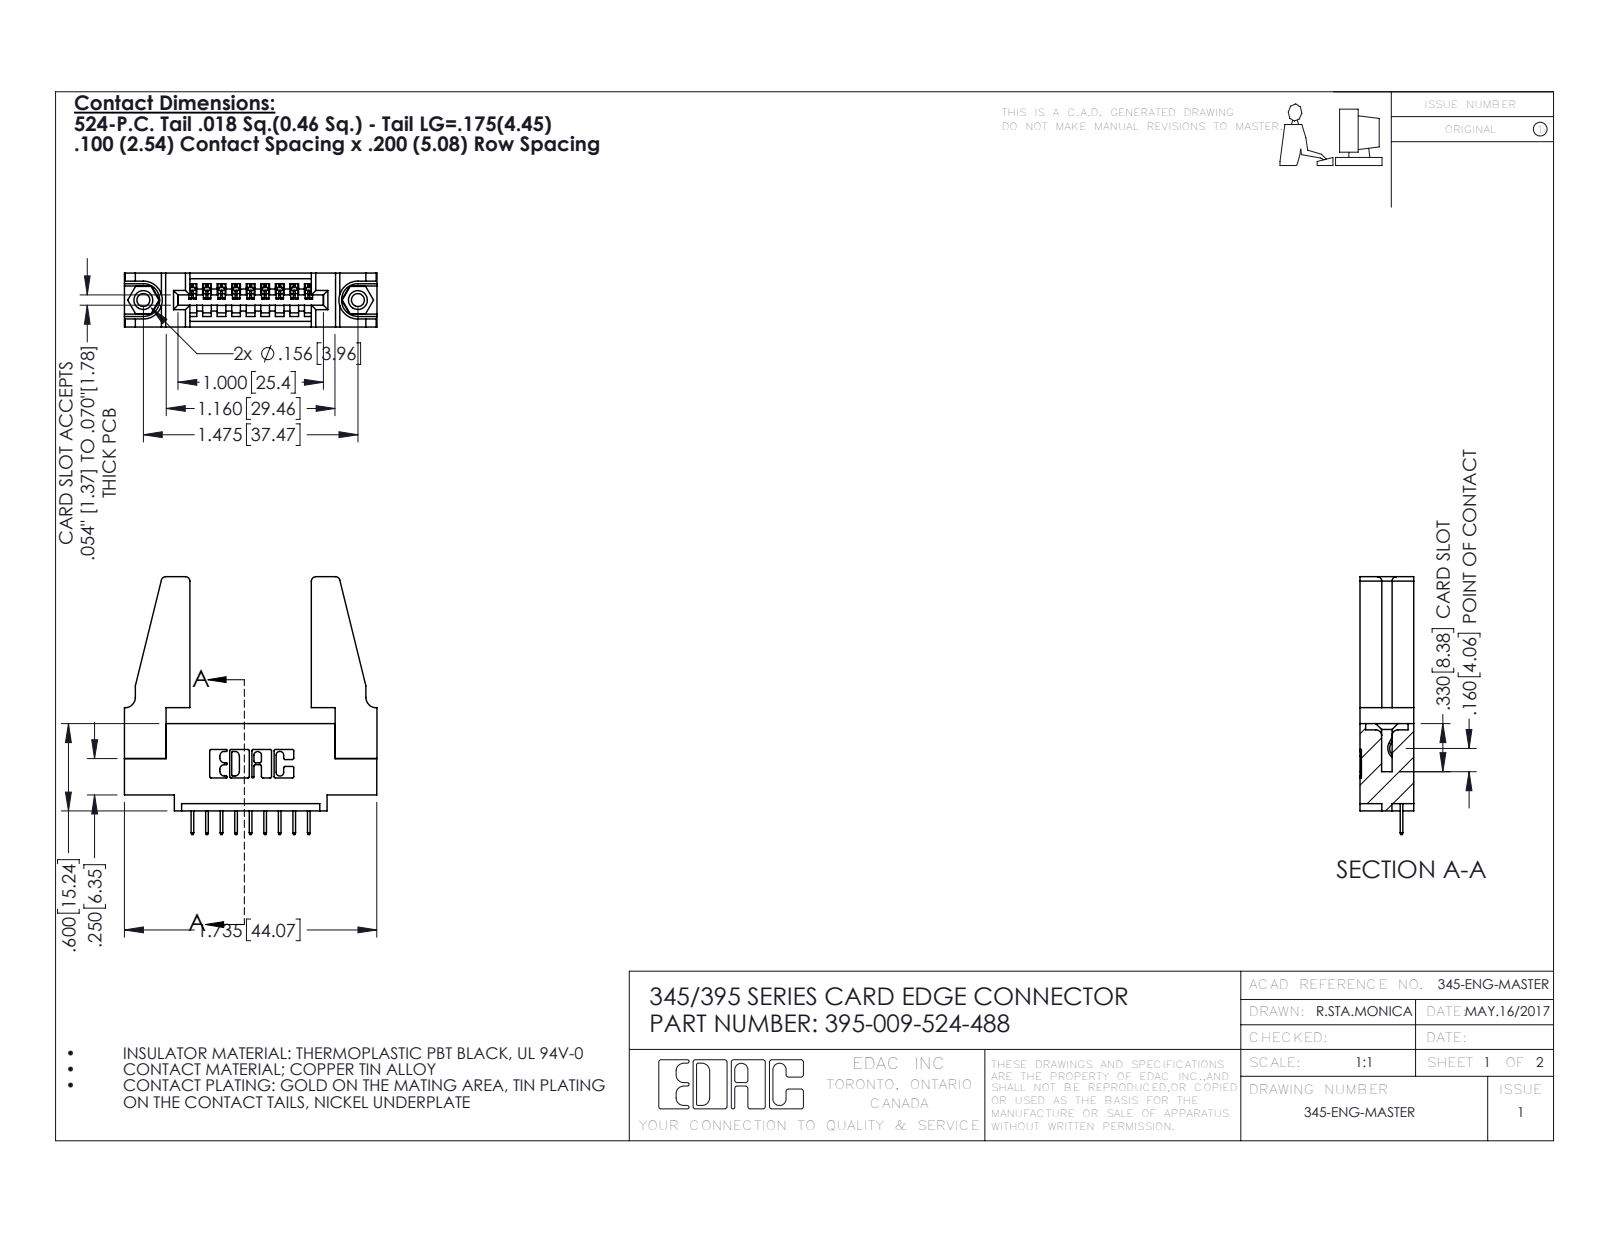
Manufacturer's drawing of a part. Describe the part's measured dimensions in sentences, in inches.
The part is named "345-220-078_345-220-088; 345-292-001_345-293-124; 345 Part_0.110 Offset - 0.156 Dia-TH; 345-250-001_345-250-001-102 (+1 more)". Its 3-D file was written by "SolidWorks 2016 (CONFIG_CONTROL_DESIGN)". It is 14 solids with 812 faces: 570 planar, 226 cylindrical and 16 other. Overall it measures 1.772 by 1.736 by 0.37 inches. Its volume is 0.431 cubic inches and its surface area 11.95 square inches. Round holes: 2 of diameter 0.089, 2 of diameter 0.125, 2 of diameter 0.156, 1 of diameter 0.064. Round bosses or shafts: 2 of diameter 0.155. Partial cylindrical surfaces (rounded edges, fillets, slot ends): 22 of radius 0.01, 18 of radius 0.006, 8 of radius 0.03, 6 of radius 0.007, 6 of radius 0.031, 3 of radius 0.026, 2 of radius 0.031, 2 of radius 0.04. The main face-to-face distances are 0.37, 0.072, 0.298, 0.2, 0.098, 0.272, 0.025, 0.15, 0.148, 0.225. The hole center spacings are 0.27, 1.244, 1.475.
